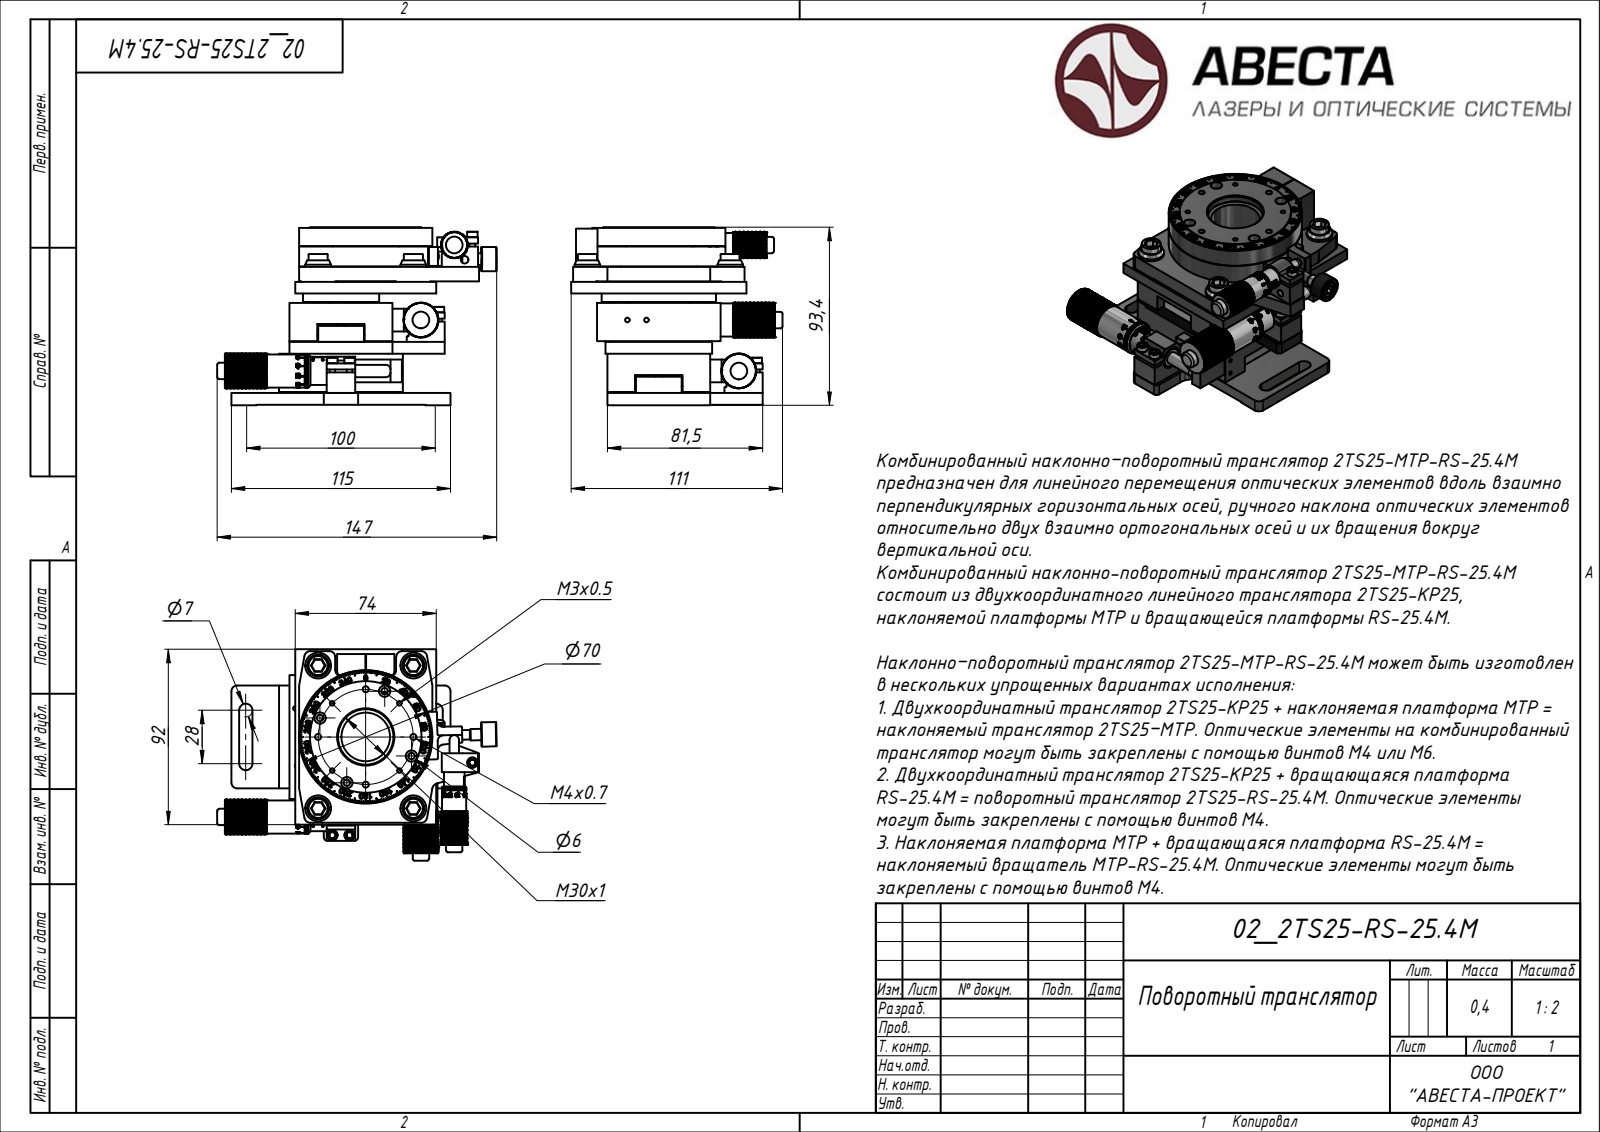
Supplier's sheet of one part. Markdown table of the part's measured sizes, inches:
| quantity | value |
| --- | --- |
| STEP written by | Rhino 7.34 (AUTOMOTIVE_DESIGN) |
| units | inches |
| bodies | 1310 solids, 17353 faces (14592 planar, 1295 cylindrical, 1466 other) |
| overall size | 5.78 × 4.37 × 3.677 |
| volume | 23.8 in³ |
| surface area | 284 in² |
| round holes (diameter × count) | 0.097 × 44, 0.236 × 29, 0.138 × 15, 0.097 × 12, 0.128 × 12, 0.134 × 10, 0.197 × 10, 0.256 × 10, 0.126 × 8, 0.079 × 7, 0.11 × 6, 0.315 × 6 |
| round bosses / shafts (diameter × count) | 0.213 × 26, 0.118 × 26, 0.394 × 6, 0.177 × 6, 0.157 × 6, 0.098 × 6, 0.531 × 5, 0.236 × 5 |
| partial cylindrical surfaces (radius × count) | 0.118 × 19, 0.079 × 10, 0.025 × 9, 0.128 × 8, 0.02 × 7, 0.048 × 5, 0.048 × 5, 0.138 × 4 |
| main face-to-face distances | 1.051, 0.807, 0.244, 0.551, 0.256, 0.795, 2.291, 0.433, 1.484, 2.602 |
| hole center spacings | 0.61, 0.394, 0.984, 1.116, 1.67, 1.969, 0.754, 1.392 |
